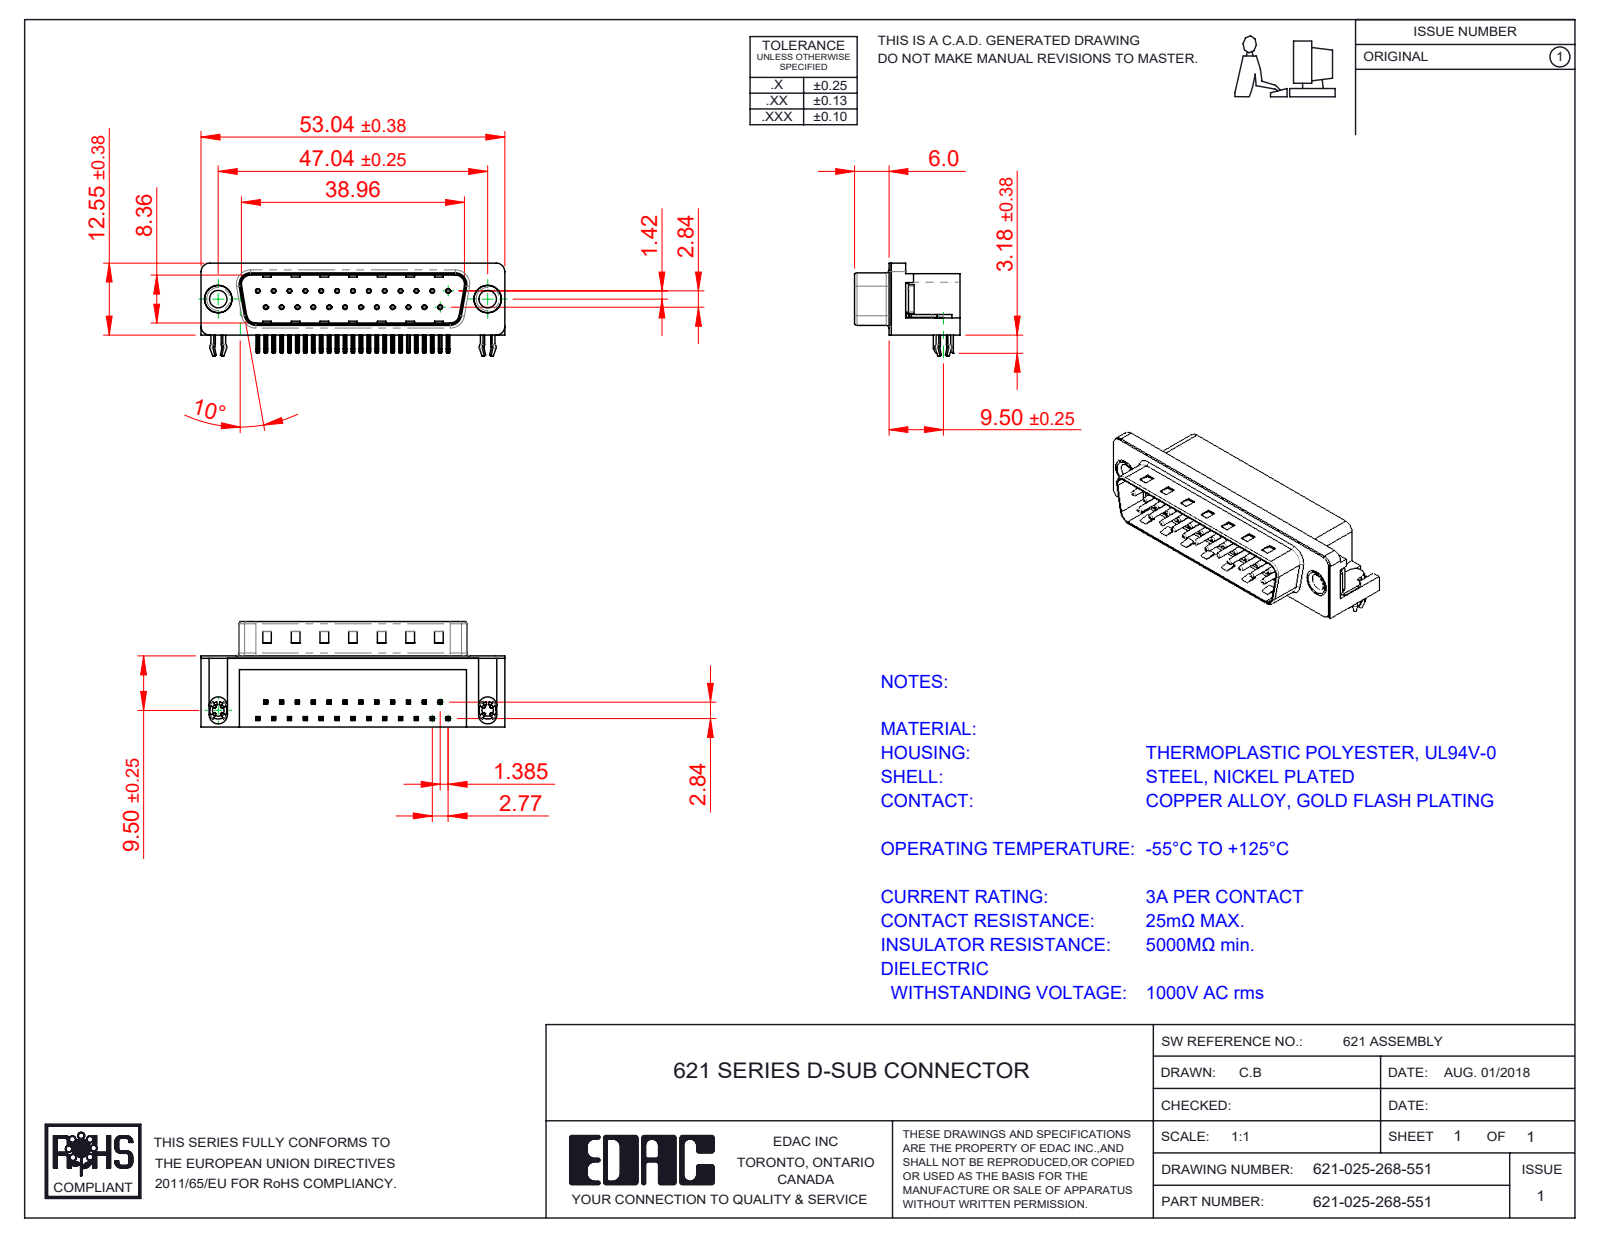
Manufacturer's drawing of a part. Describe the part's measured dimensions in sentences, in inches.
The part is named "621 4-40 Threaded Board Mount; 621 Housing_25 Socket; 621-025-268-551; 621 Shell_25 Socket (+3 more)". Its 3-D file was written by "SolidWorks 2016 (CONFIG_CONTROL_DESIGN)". It is 31 solids with 2253 faces: 1405 planar, 653 cylindrical and 195 other. Overall it measures 2.088 by 0.724 by 0.619 inches. Its volume is 0.387 cubic inches and its surface area 11.99 square inches. Round holes: 25 of diameter 0.014, 25 of diameter 0.031, 2 of diameter 0.089, 2 of diameter 0.12, 2 of diameter 0.157, 2 of diameter 0.189, 2 of diameter 0.197. Round bosses or shafts: 25 of diameter 0.03, 2 of diameter 0.193, 2 of diameter 0.187, 2 of diameter 0.152, 2 of diameter 0.128. Partial cylindrical surfaces (rounded edges, fillets, slot ends): 108 of radius 0.01, 50 of radius 0.005, 16 of radius 0.039, 9 of radius 0.02, 8 of radius 0.063, 7 of radius 0.059, 4 of radius 0.035, 4 of radius 0.079. The main face-to-face distances are 0.016, 0.472, 0.407, 0.083, 0.345, 0.412, 0.067, 0.428, 0.488, 0.354. The hole center spacings are 0.124, 0.109, 0.218, 0.327, 0.436, 0.545, 0.654, 0.198.
